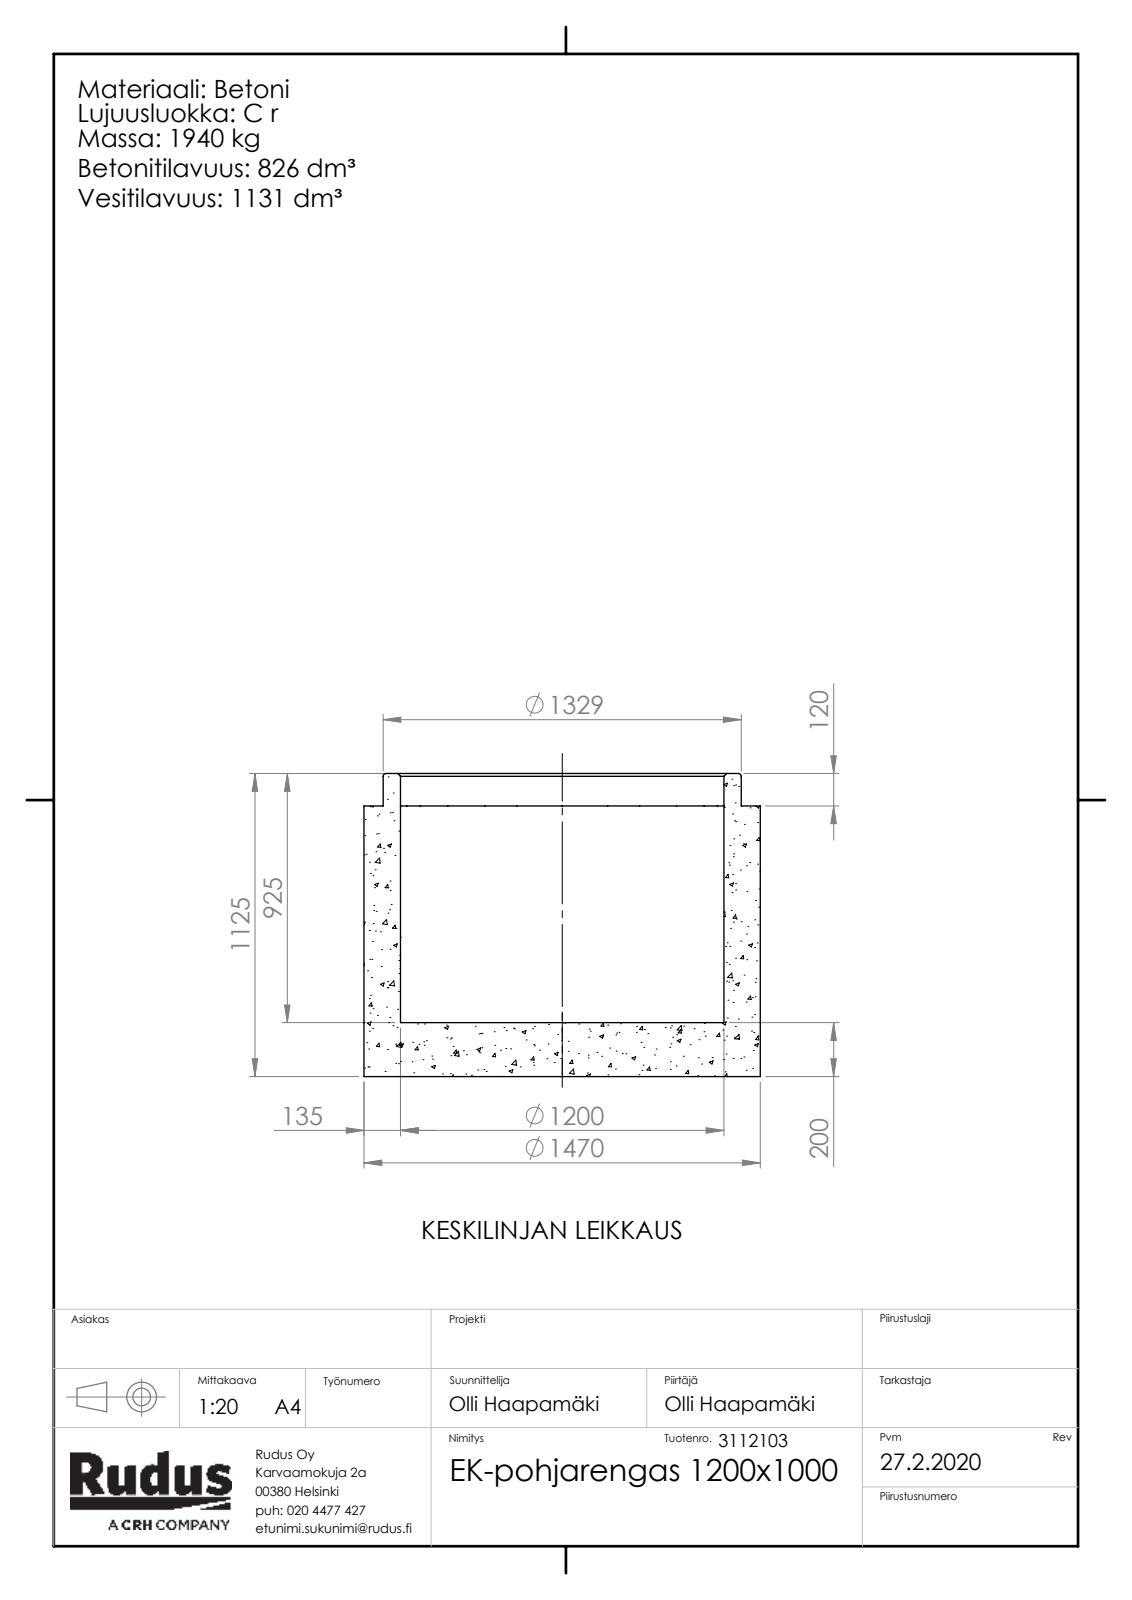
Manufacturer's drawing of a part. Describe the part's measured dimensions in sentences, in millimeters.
The part is named "EK-osa-kaivorunko_EK-pohjarengas; Rudus 3112103 EK-pohjarengas 1200x1000". Its 3-D file was written by "SolidWorks 2019 (CONFIG_CONTROL_DESIGN)". It is 1 solid with 95 faces: 4 planar, 6 cylindrical and 85 other. Overall it measures 1470 by 1470 by 1125 millimeters. Its volume is 825 600 000 cubic millimeters and its surface area 11 990 000 square millimeters. Round holes: 1 of diameter 1200. Round bosses or shafts: 1 of diameter 1470, 1 of diameter 1328.6. The main face-to-face distances are 200, 1005, 805, 1125, 925, 120.
